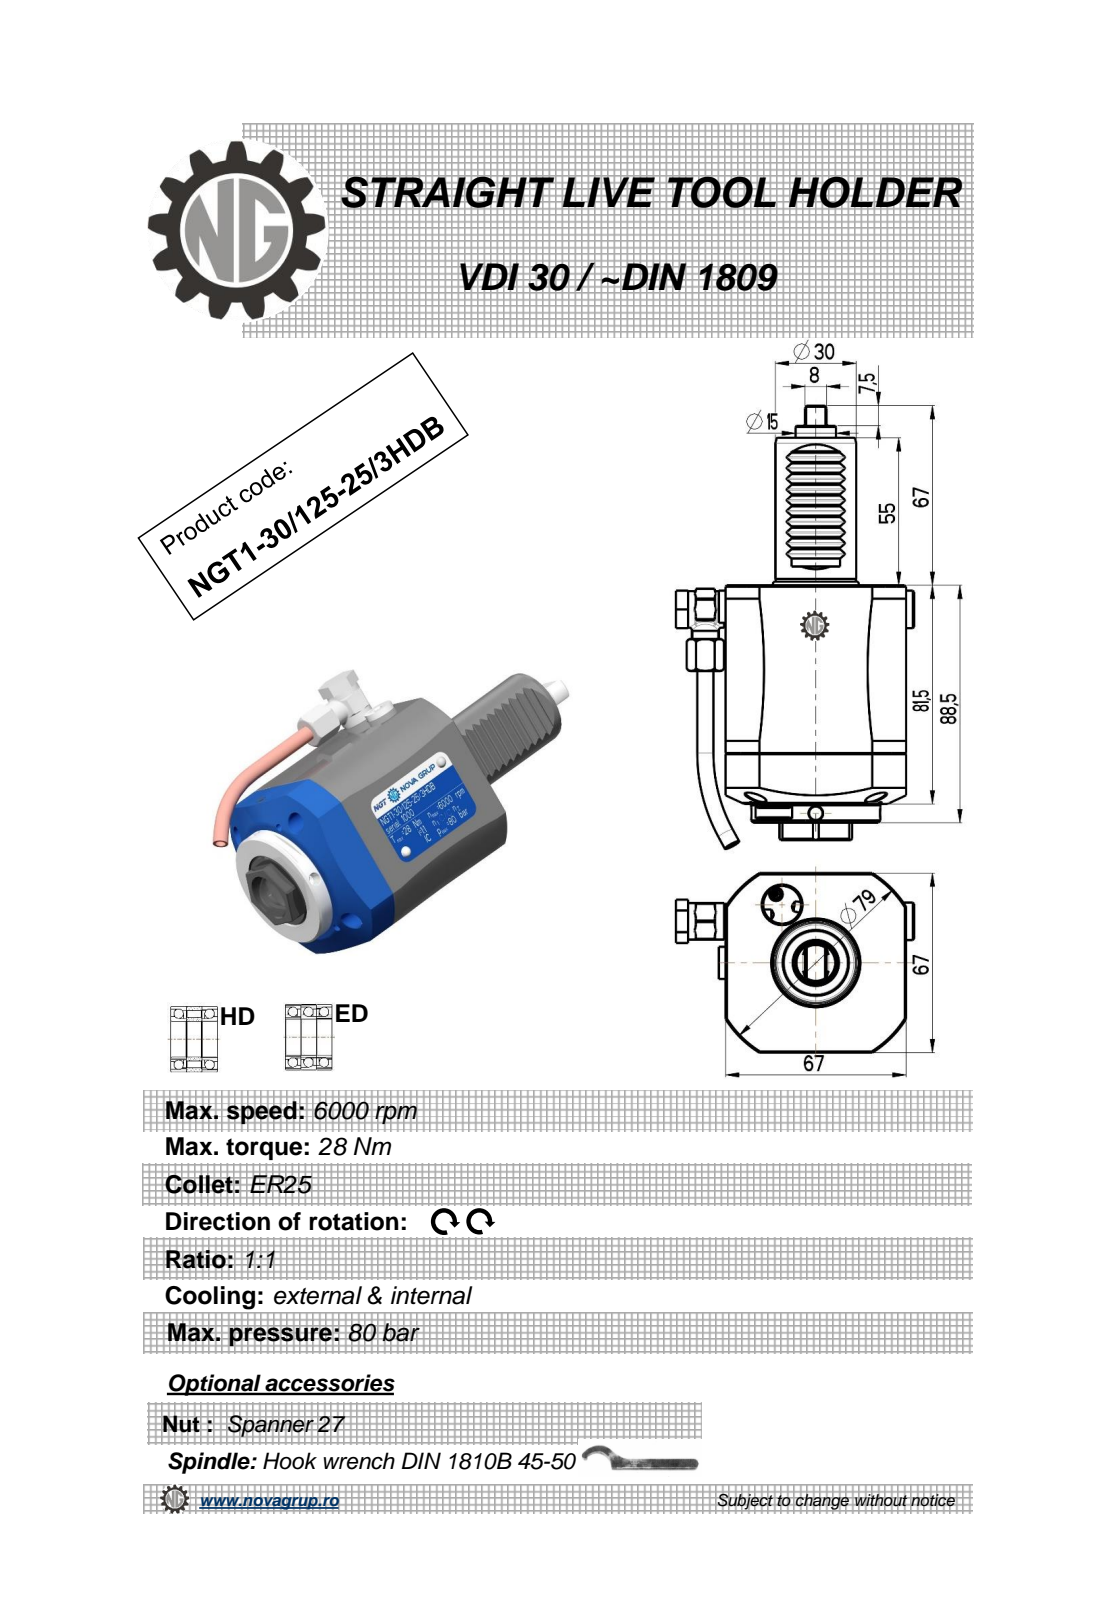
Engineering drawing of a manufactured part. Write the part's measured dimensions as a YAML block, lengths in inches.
part_name: "NGT1_30_125_25_3HDB"
step_written_by: "PRO/ENGINEER BY PARAMETRIC TECHNOLOGY CORPORATION, 2010280 (CONFIG_CONTROL_DESIGN)"
units: inches
bodies: {solids: 2, faces: 372, planar: 148, cylindrical: 105, other: 119}
overall_size: [6.509, 3.48, 2.638]
volume: 23.87
surface_area: 64.91
round_holes:
  - {diameter: 0.157, count: 3}
  - {diameter: 0.197, count: 2}
  - {diameter: 0.118, count: 1}
  - {diameter: 0.236, count: 1}
  - {diameter: 0.244, count: 1}
  - {diameter: 0.354, count: 1}
  - {diameter: 0.394, count: 1}
  - {diameter: 0.433, count: 1}
  - {diameter: 0.709, count: 1}
  - {diameter: 1.043, count: 1}
round_bosses_or_shafts:
  - {diameter: 1.89, count: 1}
  - {diameter: 1.181, count: 1}
  - {diameter: 0.591, count: 1}
  - {diameter: 0.551, count: 1}
  - {diameter: 0.535, count: 1}
  - {diameter: 0.512, count: 1}
  - {diameter: 0.472, count: 1}
  - {diameter: 0.394, count: 1}
partial_cylinders:
  - {radius: 0.012, count: 10}
  - {radius: 0.016, count: 6}
  - {radius: 0.02, count: 4}
  - {radius: 0.031, count: 2}
  - {radius: 0.283, count: 1}
  - {radius: 0.303, count: 1}
  - {radius: 1.555, count: 1}
face_to_face_distances: [2.638, 3.484, 0.276, 3.209, 0.111, 2.165, 0.223, 0.472, 5.65, 5.374]
hole_center_spacings: [0.016, 1.726, 1.741, 3.054]
